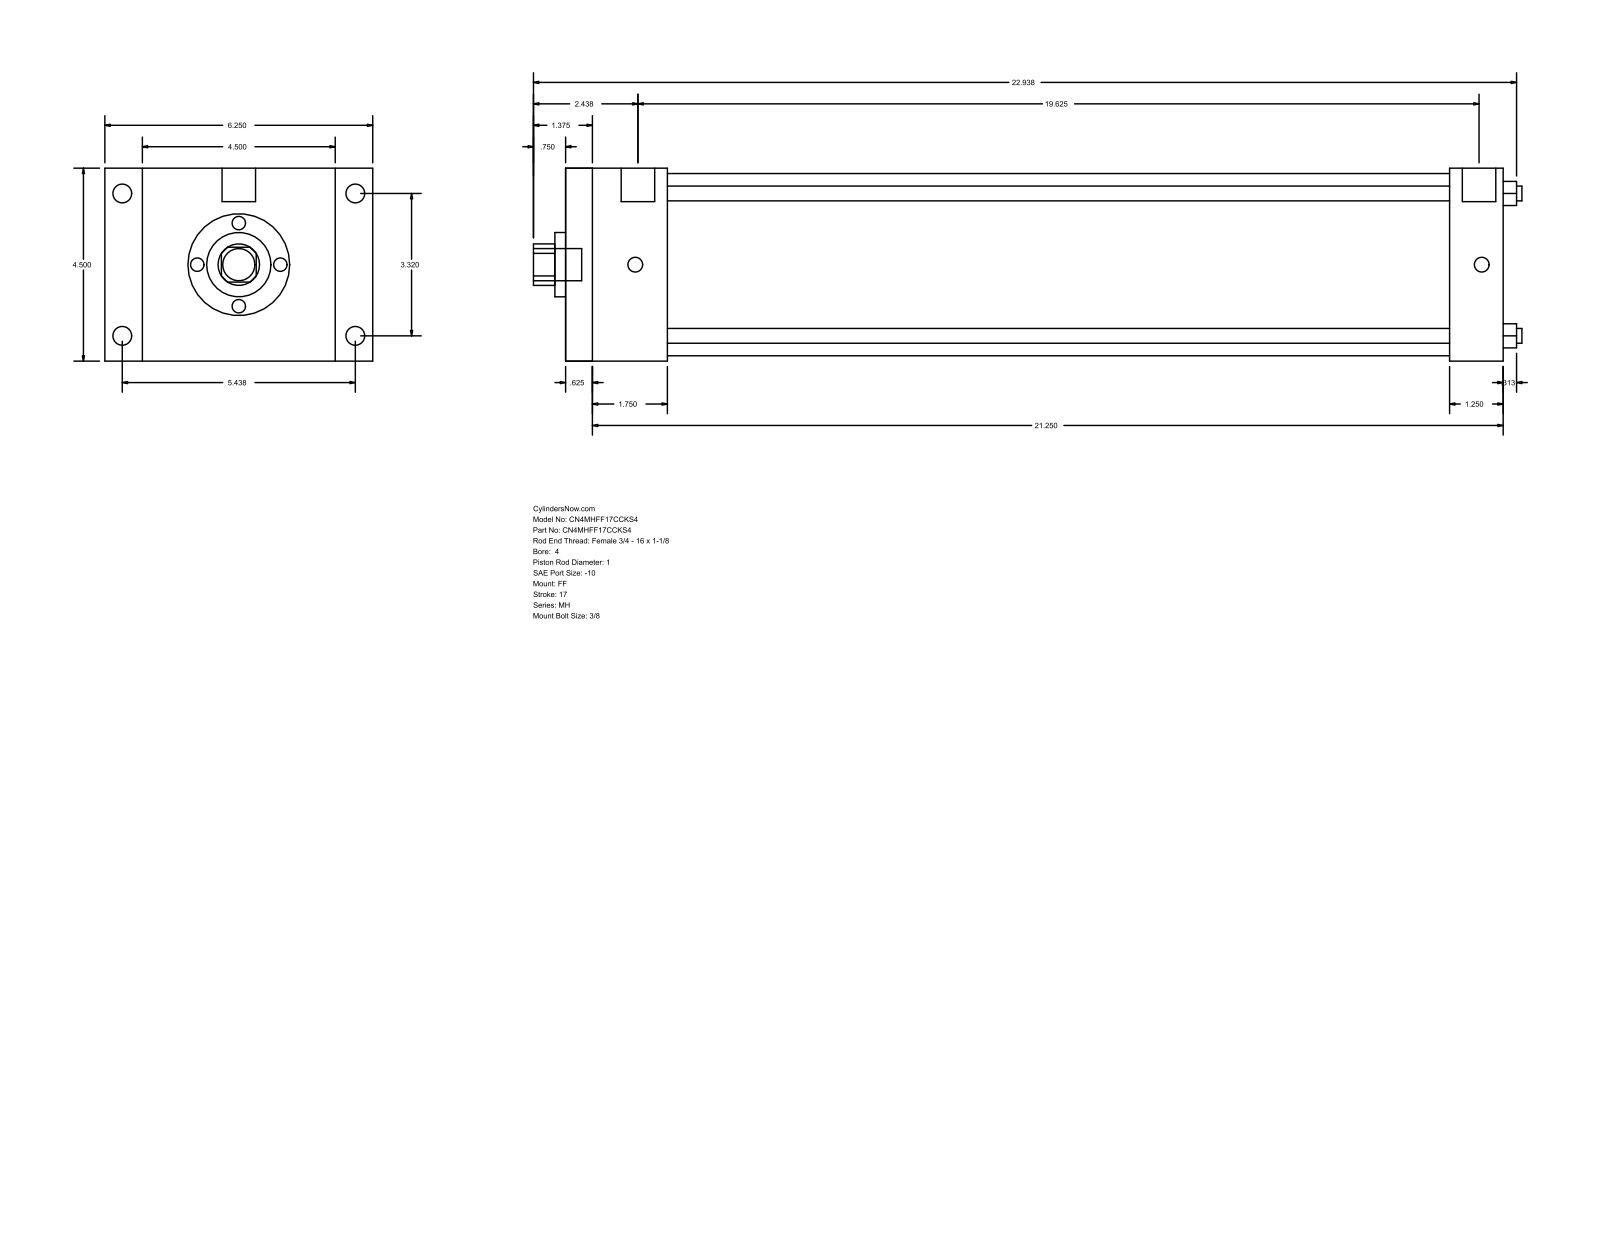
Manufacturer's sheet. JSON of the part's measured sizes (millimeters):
{"part_name": "MH_FF__0400_1", "step_written_by": "GSSL Pune (CONFIG_CONTROL_DESIGN)", "units": "millimeters", "bodies": {"solids": 0, "faces": 92, "planar": 64, "cylindrical": 28, "other": 0}, "overall_size": [585.79, 158.75, 114.3], "round_holes": [[8.76, 4], [25.4, 1], [38.1, 1], [107.95, 1]], "round_bosses_or_shafts": [[11.13, 4], [8.73, 4], [19.84, 2], [19.05, 1]], "partial_cylinders_radius": [[12.29, 1]], "face_to_face_distances": [114.3, 555.62, 15.87, 539.75, 60.33, 44.46, 495.29, 523.87, 508, 463.54], "hole_center_spacings": [59.62, 84.32, 119.25]}
